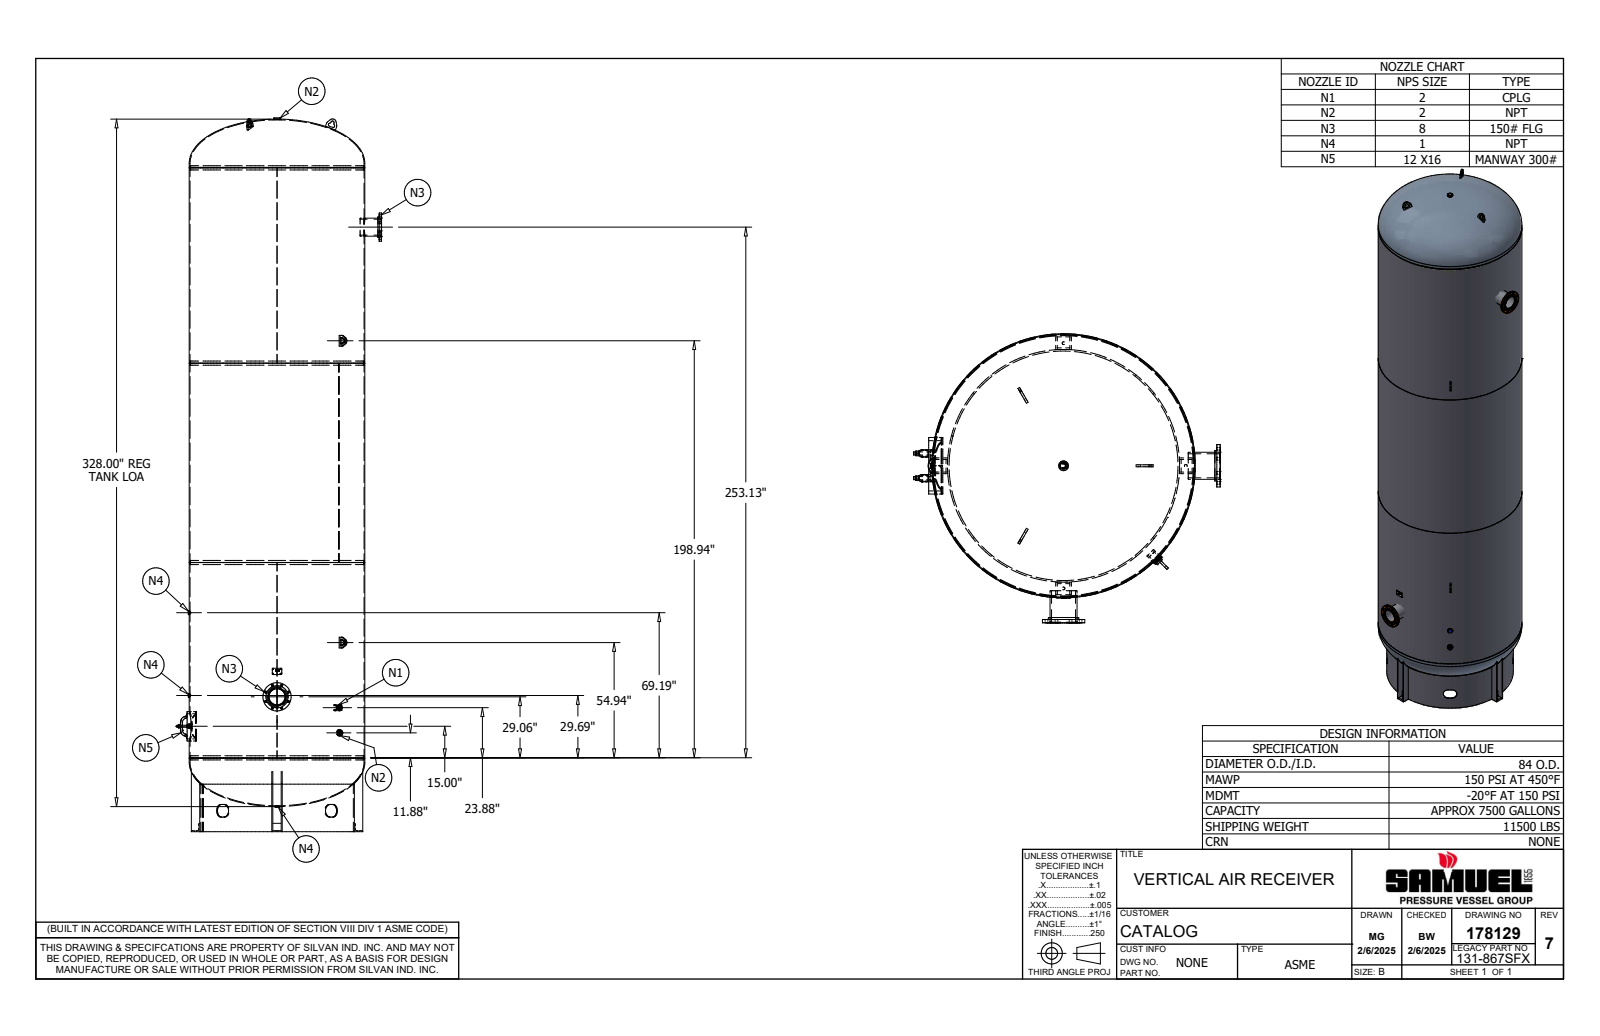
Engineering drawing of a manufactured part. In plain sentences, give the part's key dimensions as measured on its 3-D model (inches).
The part is named "178129; 237422; 237423; 237425 (+8 more)". Its 3-D file was written by "Autodesk Inventor 2022 (AUTOMOTIVE_DESIGN)". It is 62 solids with 1176 faces: 568 planar, 266 cylindrical and 342 other. Overall it measures 340.531 by 97.812 by 92 inches. Its volume is 38 094 cubic inches and its surface area 201 314 square inches. Round holes: 20 of diameter 0.875, 4 of diameter 0.375, 3 of diameter 1.193, 2 of diameter 0.865, 2 of diameter 1, 2 of diameter 1.125, 2 of diameter 2, 2 of diameter 2.172, 2 of diameter 7.625, 2 of diameter 8, 2 of diameter 8.625, 1 of diameter 2.231. Round bosses or shafts: 3 of diameter 2, 3 of diameter 1.563, 2 of diameter 13.5, 2 of diameter 10.625, 2 of diameter 9.69, 2 of diameter 3, 2 of diameter 2.205, 2 of diameter 1. Partial cylindrical surfaces (rounded edges, fillets, slot ends): 29 of radius 0.75, 15 of radius 1.75, 12 of radius 0.06, 12 of radius 0.5, 12 of radius 0.776, 10 of radius 0.375, 7 of radius 3, 6 of radius 1. The main face-to-face distances are 0.5, 4.5, 2, 4, 5, 1.063, 39, 188.313, 2.5, 93.187. The hole center spacings are 4.496, 5.875, 10.856, 8.308, 8.309, 4.497, 5.875, 10.856.
